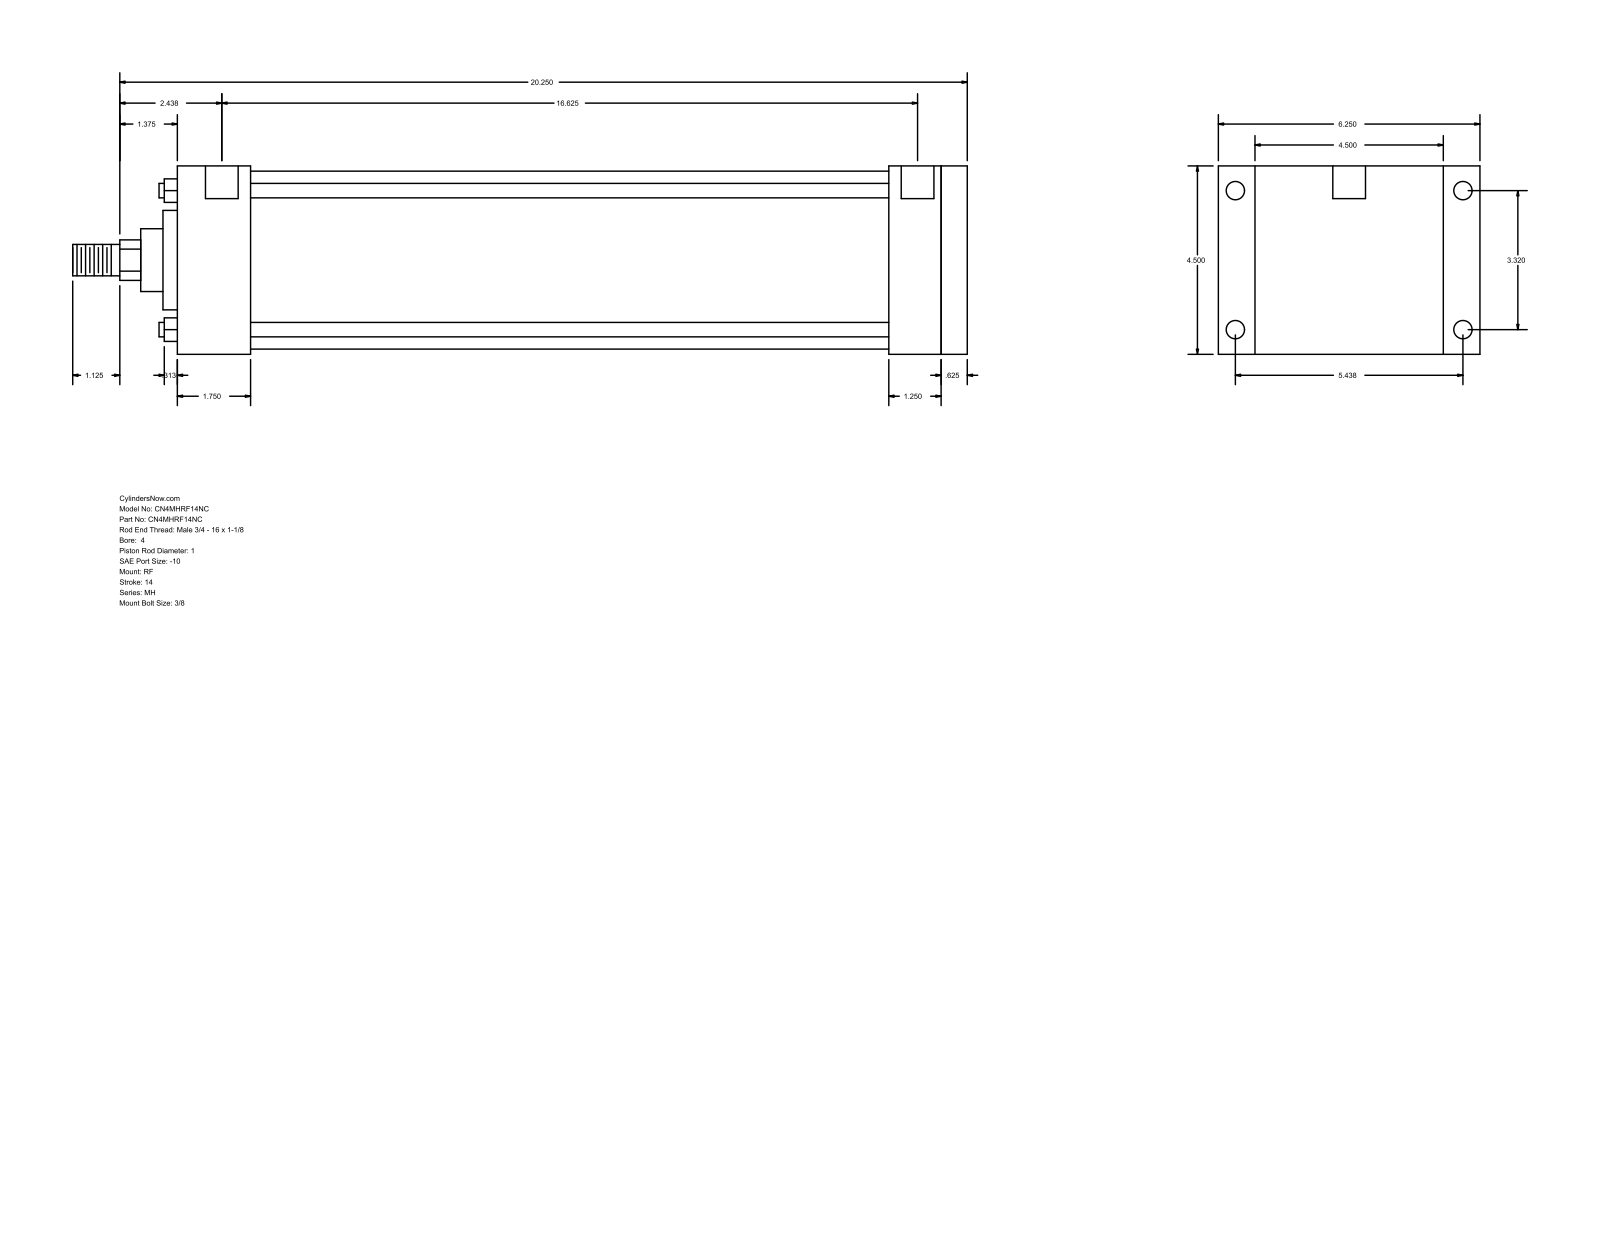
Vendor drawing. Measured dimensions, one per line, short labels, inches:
name: MH_RF__0400_1
written by: GSSL Pune (CONFIG_CONTROL_DESIGN)
unit: in
bodies: 0 solids, 94 faces (65 planar, 29 cylindrical, 0 other)
size: 21.375 × 6.25 × 4.5
holes: 4× ⌀0.344, 4× ⌀0.438, 2× ⌀0.781
bosses: 4× ⌀0.345, 1× ⌀4.25, 1× ⌀2.375, 1× ⌀1.5, 1× ⌀1, 1× ⌀0.75
rounds: 1× R0.484
face distances: 4.5, 18.875, 18.25, 0.625, 1.75, 16.5, 17.125, 17, 15.25, 1.25
hole spacings: 0.062, 3.32, 5.438, 6.371, 16.687, 16.75, 16.625
